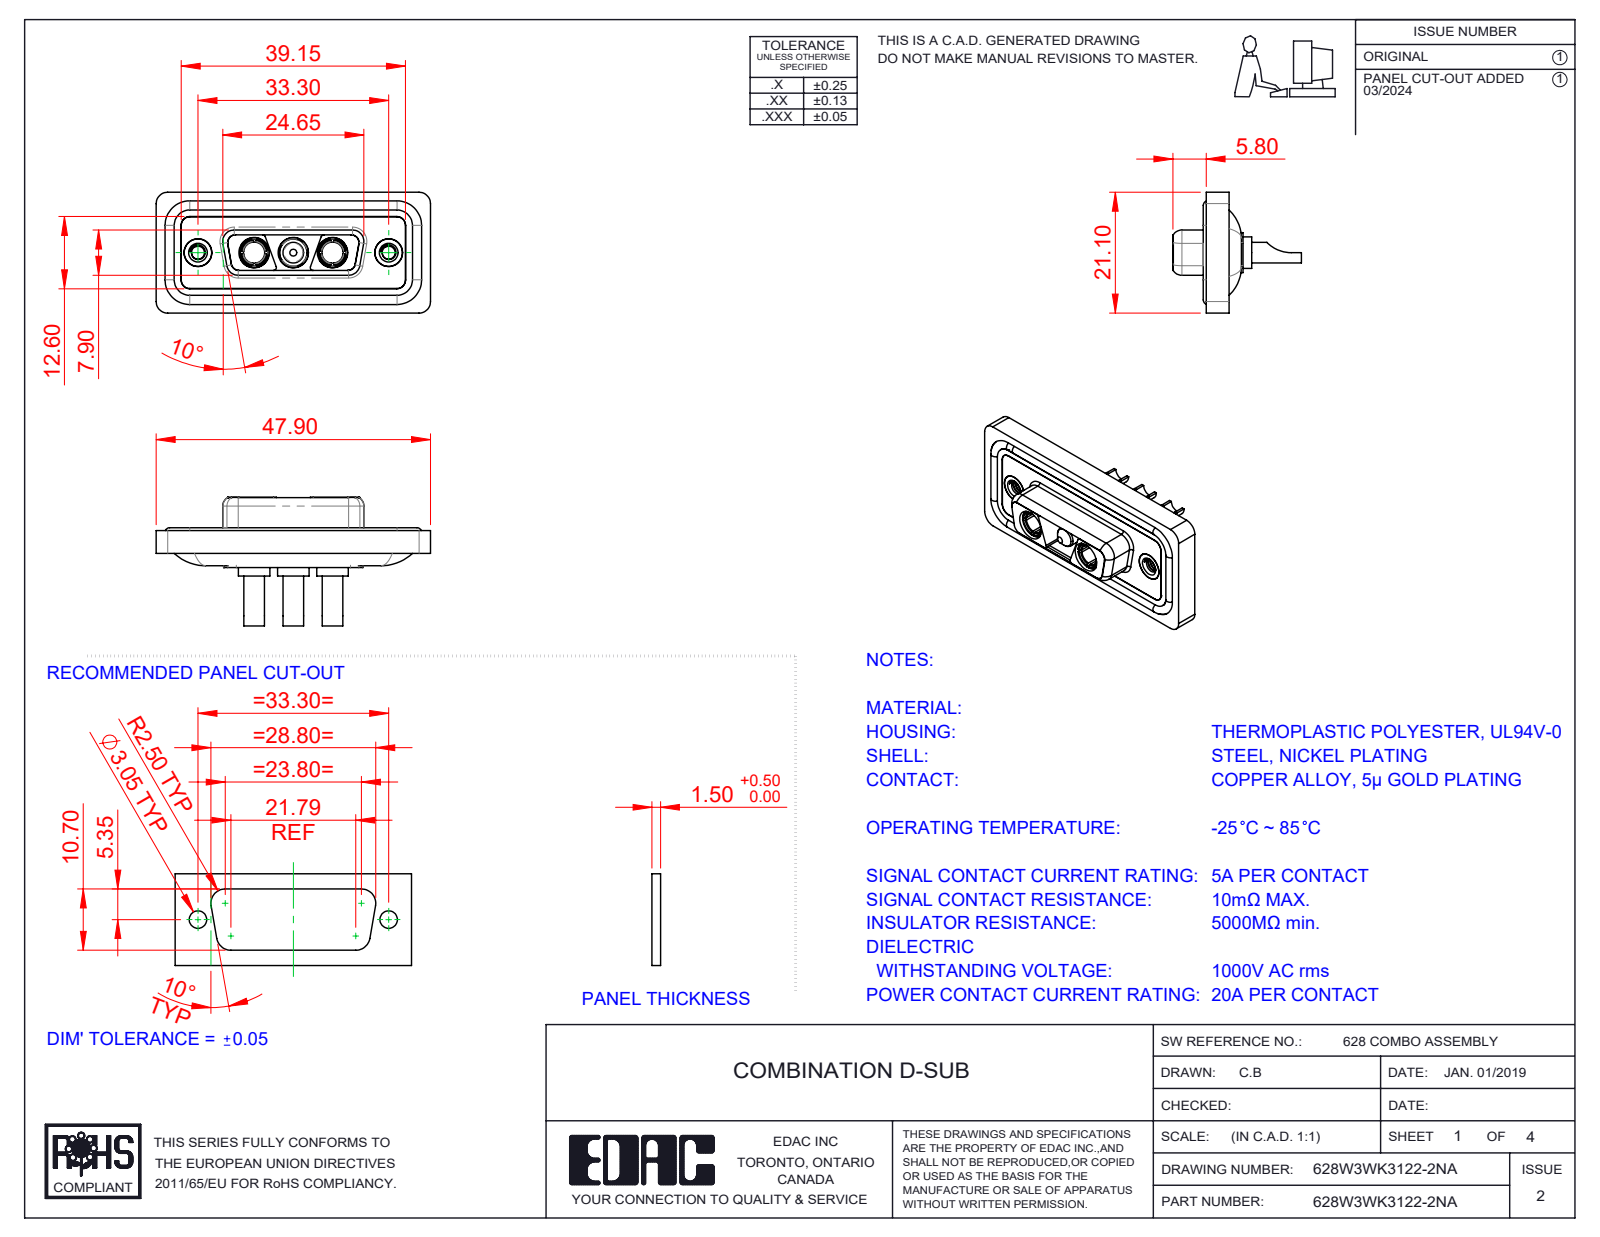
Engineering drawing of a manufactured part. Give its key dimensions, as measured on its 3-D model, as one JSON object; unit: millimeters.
{"part_name": "628W3WK3122-2NA; 628Combo Shell Rear_15 Contacts; 628Combo Shell Front_15 Contacts; 628Combo Housing_3WK3 (+4 more)", "step_written_by": "SolidWorks 2023 (CONFIG_CONTROL_DESIGN)", "units": "millimeters", "bodies": {"solids": 13, "faces": 600, "planar": 187, "cylindrical": 269, "other": 144}, "overall_size": [47.9, 22.45, 21.1], "volume_mm3": 5918, "surface_area_mm2": 9750, "round_holes": [[4.85, 5], [2.7, 3], [5.3, 3], [2.26, 2], [3.7, 2], [4, 2], [4.05, 2], [5, 2]], "round_bosses_or_shafts": [[1.6, 4], [5.5, 3], [5.2, 3], [4.75, 3], [3.75, 3], [3.6, 3], [4.96, 2], [4.95, 2]], "partial_cylinders_radius": [[1.5, 22], [2, 20], [1.35, 12], [0.5, 8], [1.6, 8], [0.25, 4], [0.6, 4], [0.65, 4]], "face_to_face_distances": [0.4, 1.6, 0.5, 1.8, 1.1, 2.9, 5.65, 7.05, 5.35, 1.5], "hole_center_spacings": [6.85, 9.8, 16.65, 23.5, 13.7, 33.3]}
